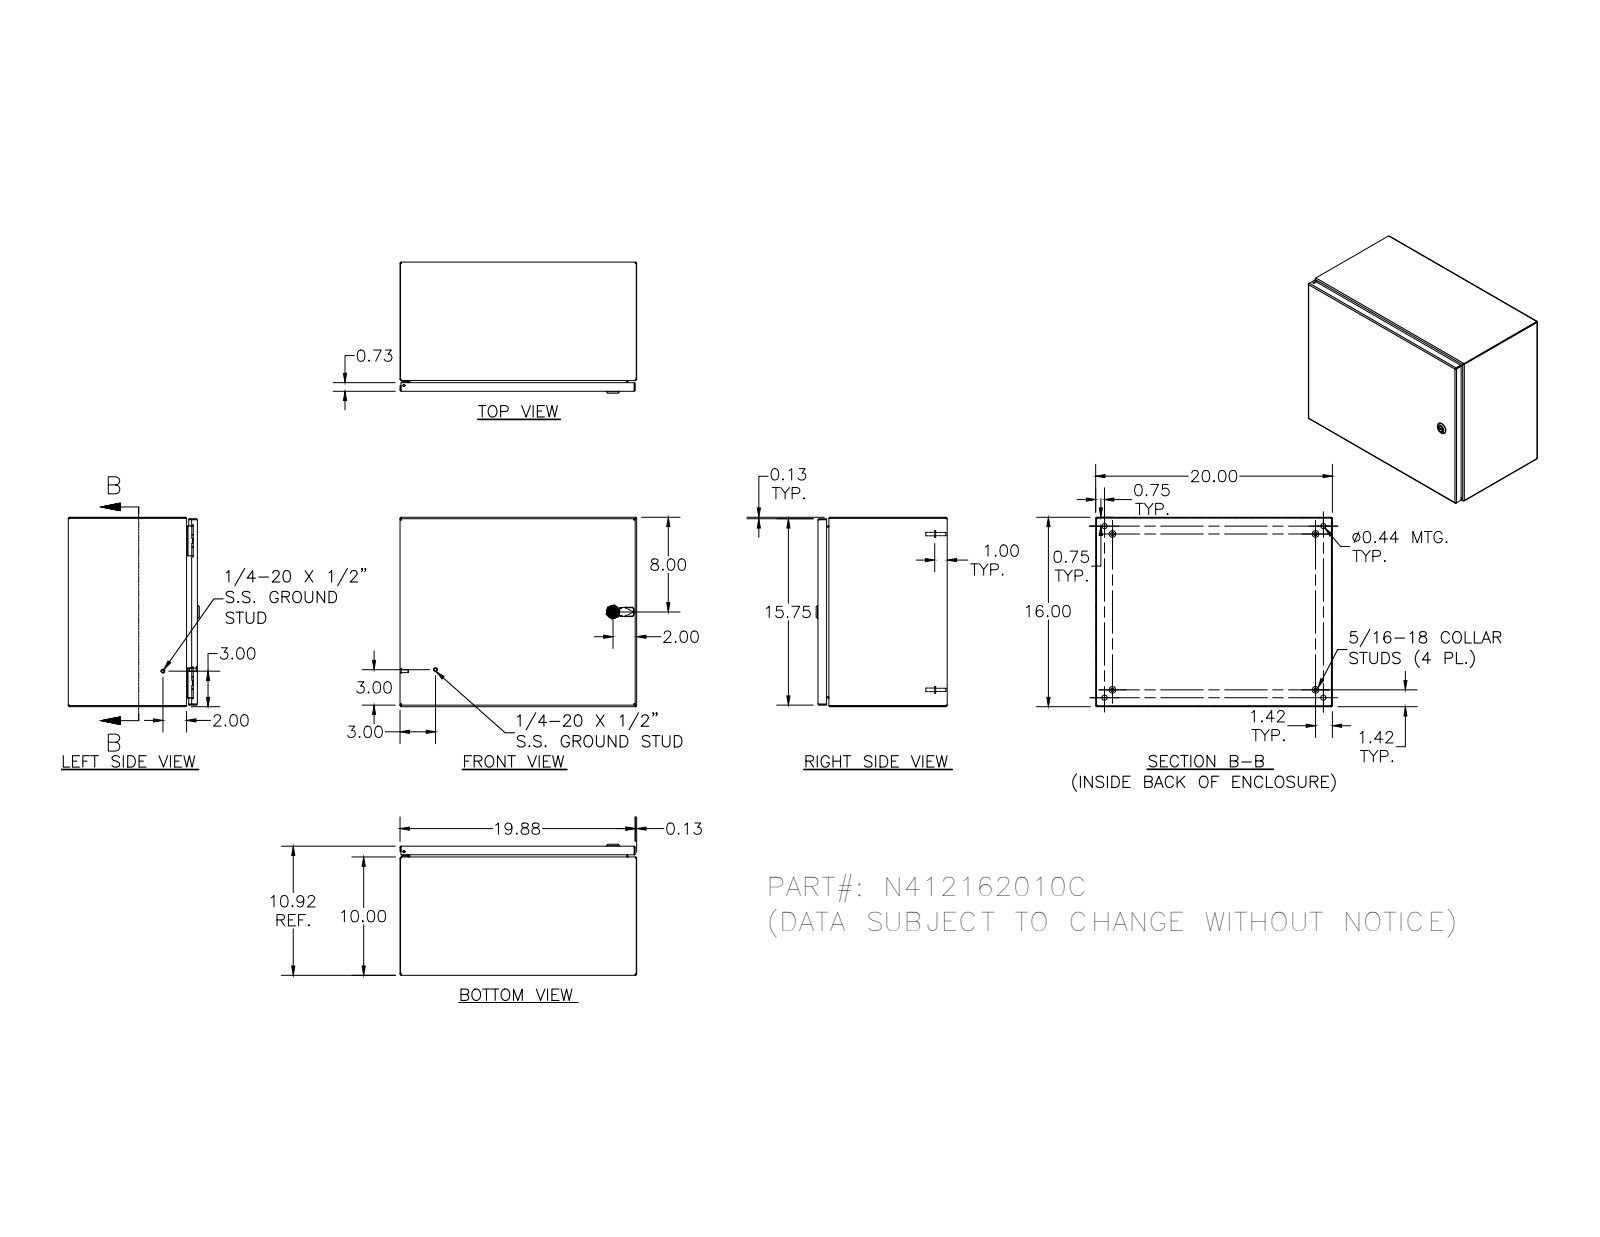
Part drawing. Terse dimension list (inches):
name: N412162010C
written by: SolidWorks 2018 (AUTOMOTIVE_DESIGN)
unit: in
bodies: 33 solids, 1449 faces (530 planar, 547 cylindrical, 372 other)
size: 20 × 16 × 11.075
volume: 111.6 in³; area: 3 035 in²
holes: 5× ⌀0.188, 4× ⌀0.093, 4× ⌀0.152, 4× ⌀0.167, 4× ⌀0.172, 4× ⌀0.437, 2× ⌀0.156, 1× ⌀0.187, 1× ⌀0.197, 1× ⌀0.315, 1× ⌀0.394, 1× ⌀0.402
bosses: 10× ⌀0.25, 4× ⌀0.563, 4× ⌀0.36, 4× ⌀0.32, 4× ⌀0.3, 4× ⌀0.275, 4× ⌀0.256, 4× ⌀0.164
rounds: 30× R0.012, 30× R0.031, 26× R0.05, 20× R0.105, 18× R0.016, 16× R0.125, 13× R0.02, 8× R0.032
face distances: 0.074, 10.843, 0.074, 10.769, 10.917, 15.926, 16, 15.852, 15.926, 19.926
hole spacings: 12, 0.66, 0.656, 1.307, 1.965, 11.34, 12.66, 0.5
